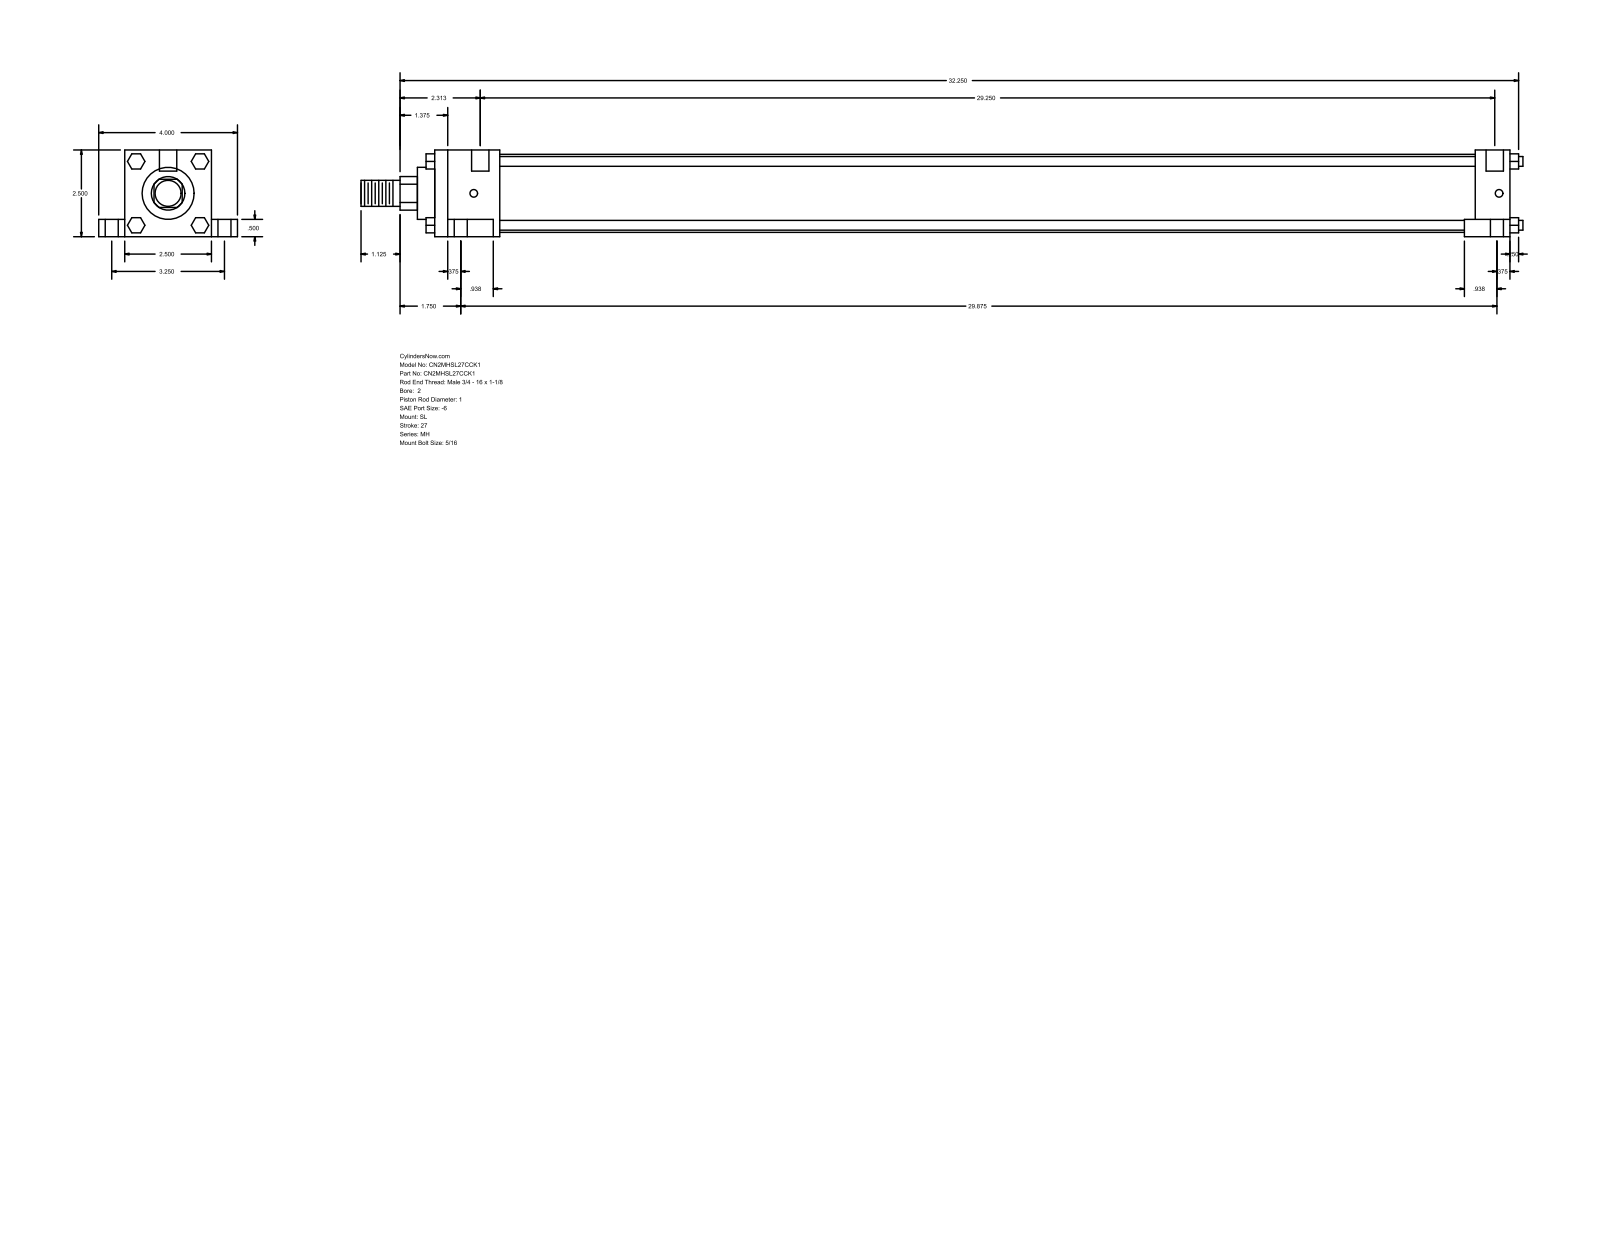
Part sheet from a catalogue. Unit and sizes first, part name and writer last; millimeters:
Units: millimetres
Overall size (bounding box): 850.9 × 101.6 × 63.5
Round holes (diameter × count): ⌀5.56 ×4, ⌀9.53 ×4, ⌀15.88 ×4, ⌀12.7 ×2
Round bosses / shafts (diameter × count): ⌀7.14 ×4, ⌀57.15 ×1, ⌀38.1 ×1, ⌀25.4 ×1, ⌀19.05 ×1
Partial cylindrical surfaces — rounded edges, fillets, slot ends (radius × count): R12.29 ×1
Main face-to-face distances: 63.5, 787.4, 12.7, 19.05, 50.8, 82.55, 25.4, 762, 47.63, 714.37
Hole centre spacings: 41.3, 42.36, 43.67, 82.54, 745.67, 750.43, 750.88, 758.36
Bodies: 0 solids, 148 faces (112 planar, 36 cylindrical, 0 other)
Part name (STEP PRODUCT): MH_SL__0200_1
STEP written by: GSSL Pune (CONFIG_CONTROL_DESIGN)
